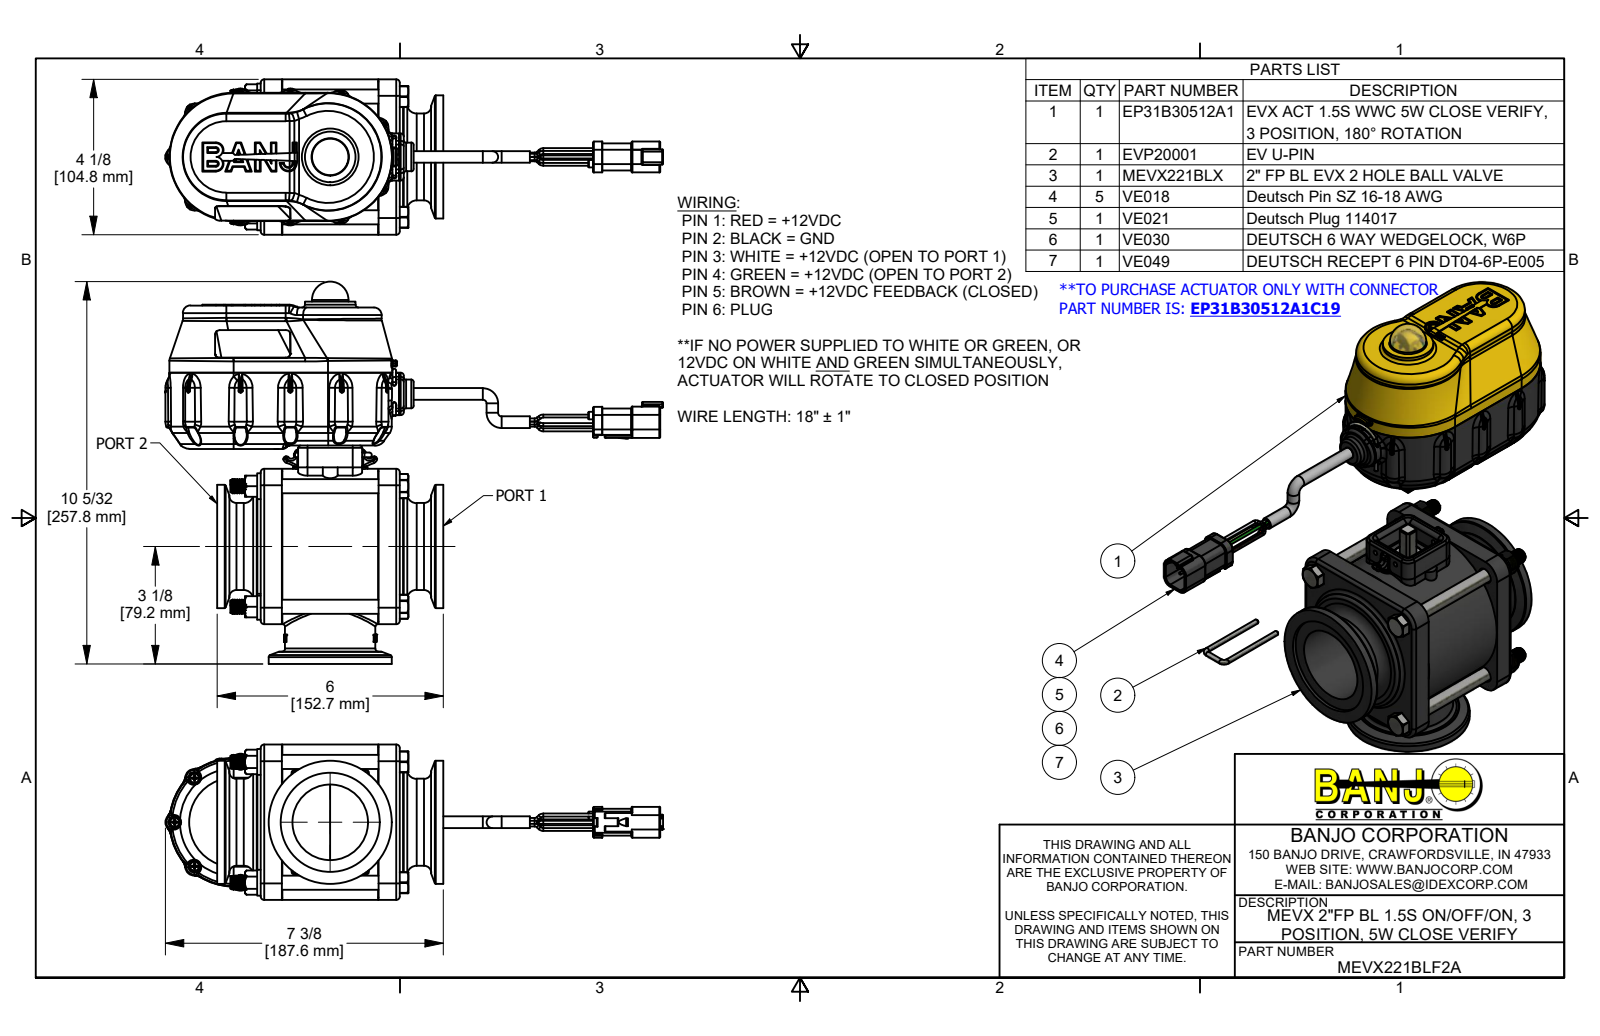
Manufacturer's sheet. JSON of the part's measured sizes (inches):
{"part_name": "MEVX221BLF2A; EP31B30512A1; B61905PPHS; B632038PM (+8 more)", "step_written_by": "Autodesk Inventor 2019 (AUTOMOTIVE_DESIGN)", "units": "inches", "bodies": {"solids": 116, "faces": 13635, "planar": 4721, "cylindrical": 3756, "other": 5158}, "overall_size": [13.218, 10.15, 4.125], "volume_in3": 102.7, "surface_area_in2": 841.1, "round_holes": [[0.095, 11], [0.15, 11], [0.08, 7], [0.05, 6], [0.148, 6], [0.165, 6], [0.061, 5], [0.107, 4], [0.126, 4], [0.136, 4], [0.15, 4], [0.17, 4]], "round_bosses_or_shafts": [[0.324, 60], [0.08, 25], [0.25, 17], [0.14, 11], [0.108, 11], [0.085, 11], [0.058, 10], [0.375, 5]], "partial_cylinders_radius": [[0.013, 180], [0.04, 145], [0.01, 123], [0.02, 114], [0.03, 57], [0.005, 49], [0.015, 37], [0.08, 28]], "face_to_face_distances": [0.1, 2.565, 0.063, 0.645, 3.045, 1.51, 1.572, 2.485, 0.56, 3.13], "hole_center_spacings": [0.175, 0.175, 0.35, 0.399, 0.399, 0.891, 0.359, 0.888]}
